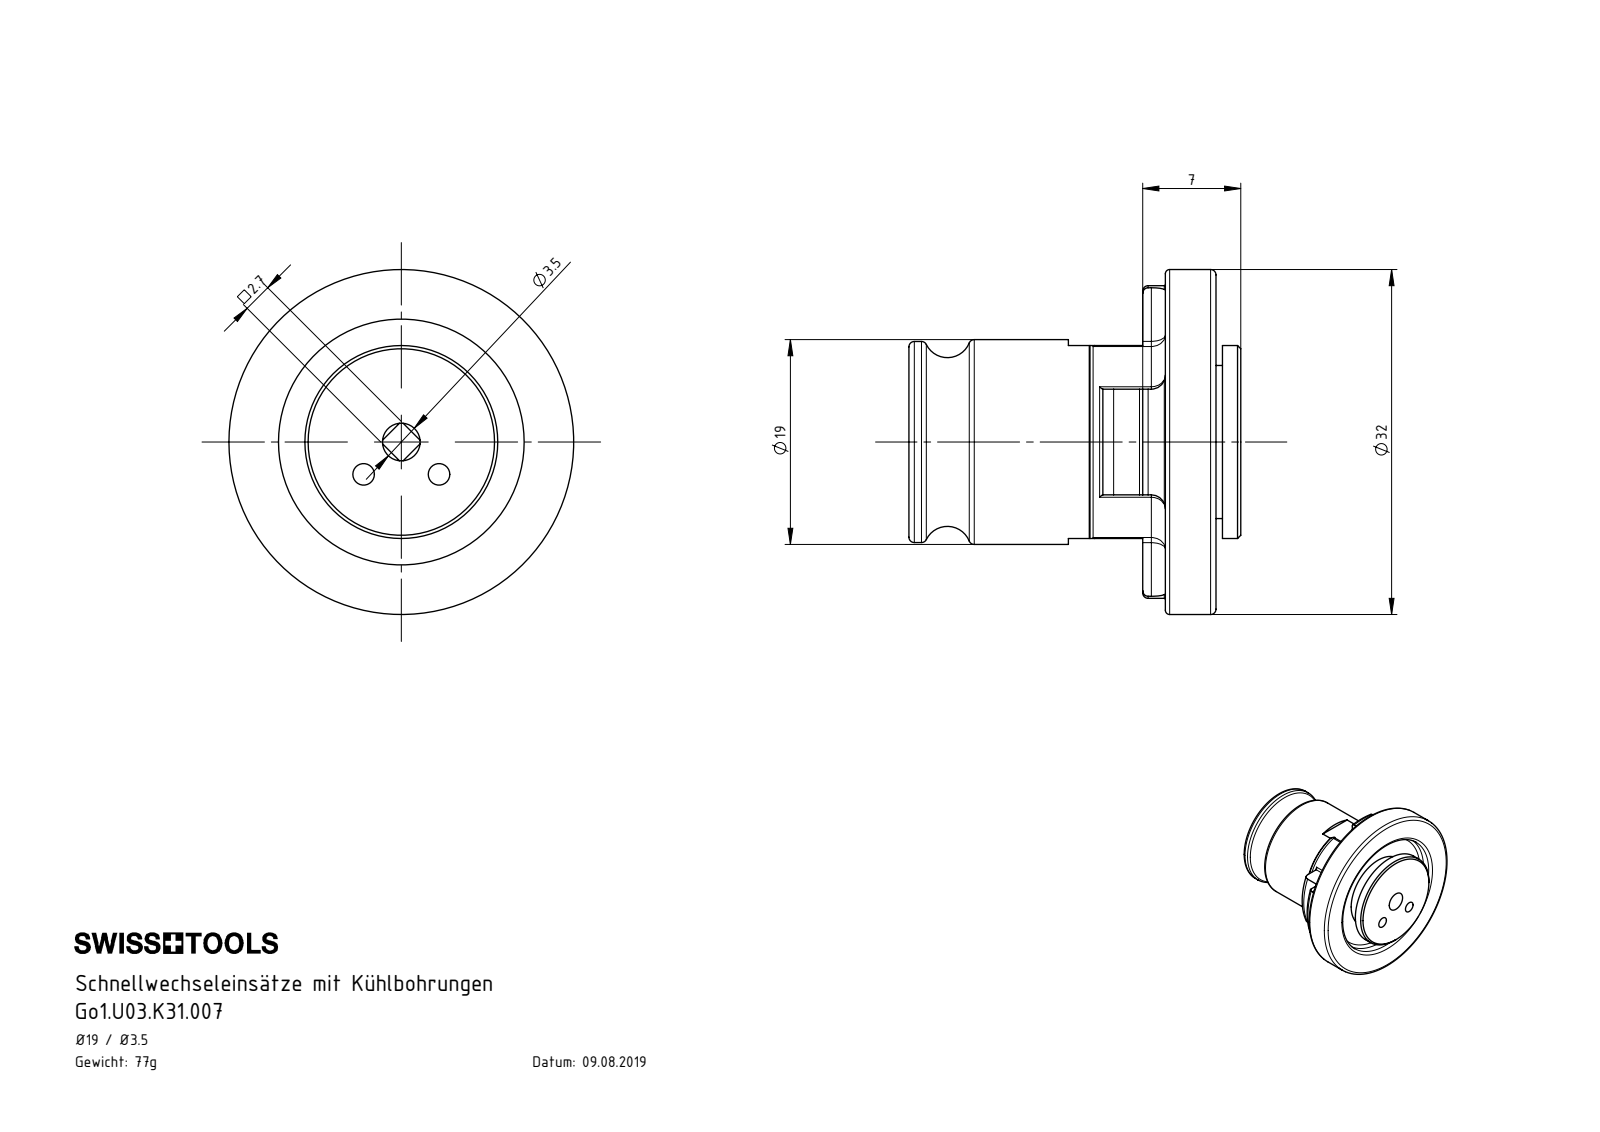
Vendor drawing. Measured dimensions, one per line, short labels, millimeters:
name: Go1.U03.K31.007
written by: SolidWorks 2017 (AUTOMOTIVE_DESIGN)
unit: mm
bodies: 1 solid, 114 faces (36 planar, 34 cylindrical, 44 other)
size: 32 × 32 × 30.8
volume: 9 772 mm³; area: 4 766 mm²
holes: 2× ⌀2, 1× ⌀3.5, 1× ⌀11.4, 1× ⌀22.8
bosses: 1× ⌀32, 1× ⌀19, 1× ⌀18.65, 1× ⌀18.52, 1× ⌀17.9, 1× ⌀14.2
rounds: 8× R0.5, 4× R1.3, 1× R12.4, 1× R14.5
face distances: 2.35, 4.7, 7, 2.3, 4.65, 23.8, 26.15, 28.5, 30.8, 29.1
hole spacings: 4.61, 7
